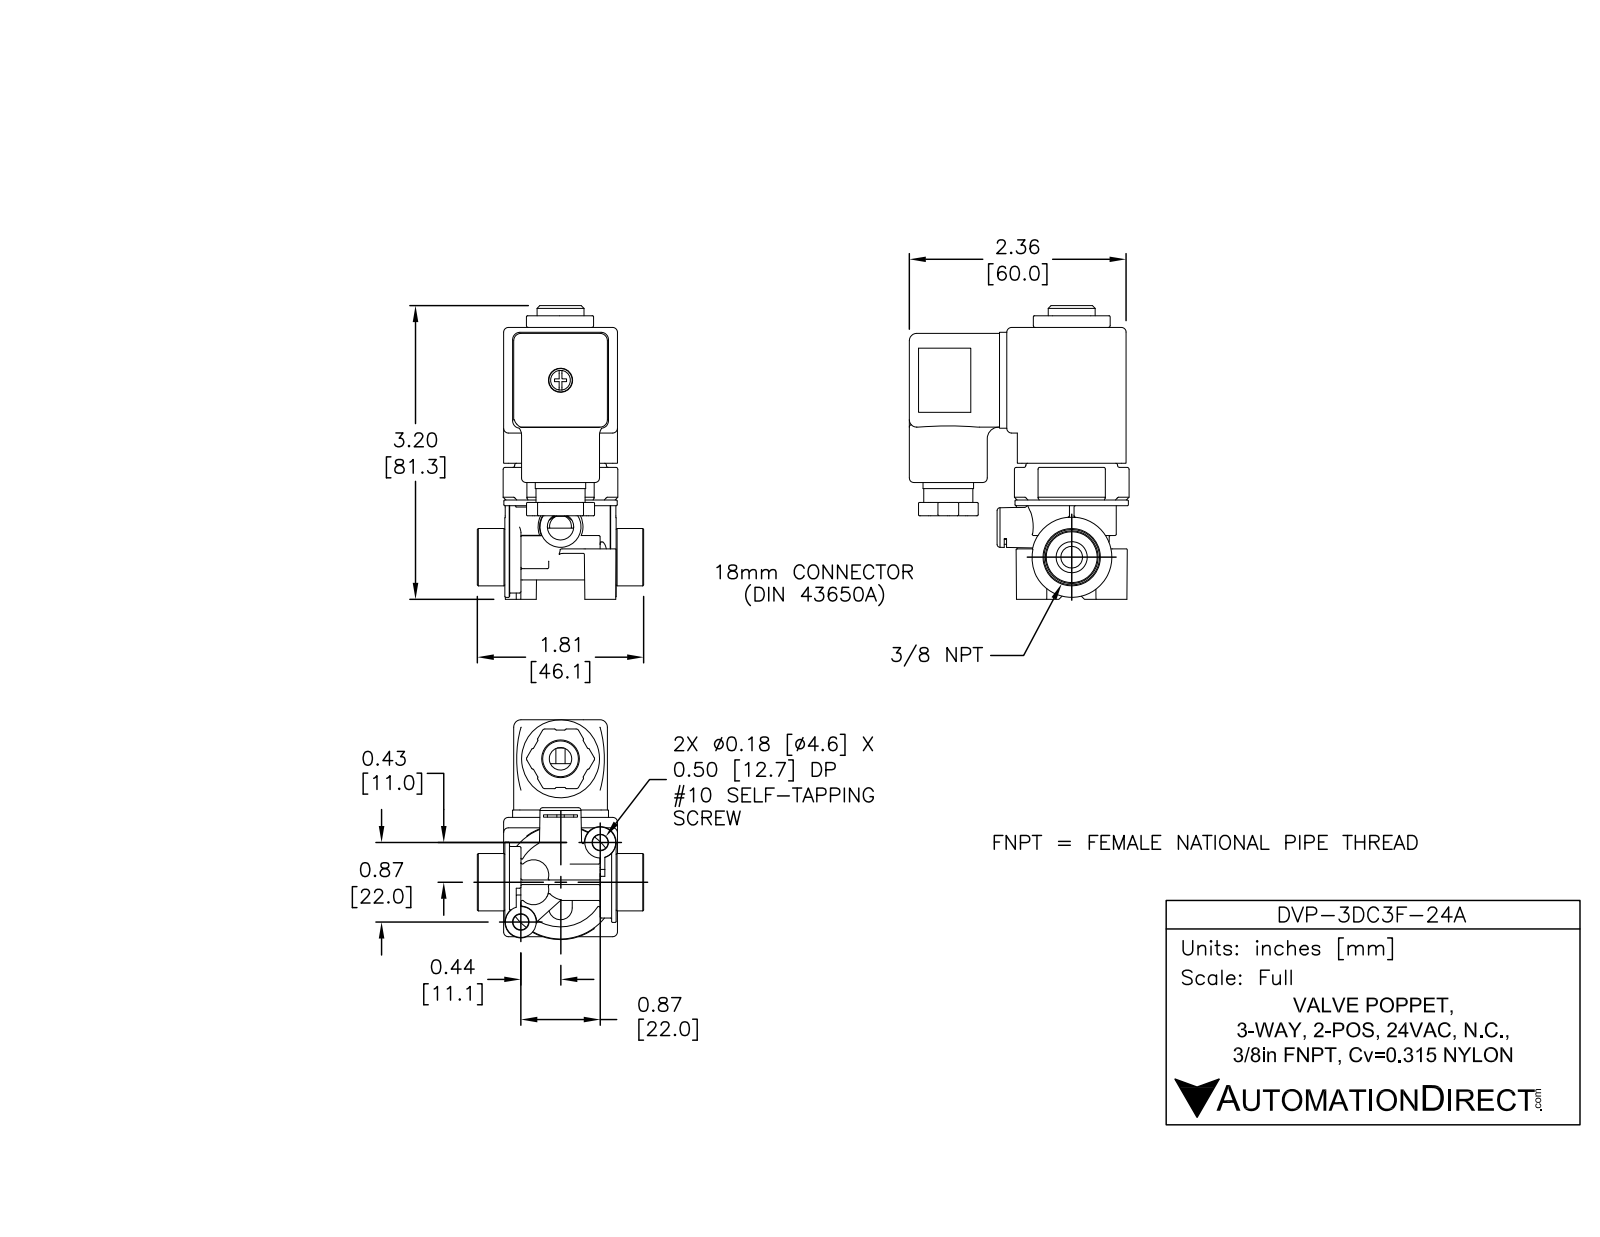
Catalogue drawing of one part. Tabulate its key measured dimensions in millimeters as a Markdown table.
| quantity | value |
| --- | --- |
| part name | DVP-3DC3F-24A |
| STEP written by | SolidWorks 2015 (AUTOMOTIVE_DESIGN) |
| units | millimeters |
| bodies | 6 solids, 1790 faces (806 planar, 344 cylindrical, 640 other) |
| overall size | 81.4 × 60.8 × 46.1 |
| volume | 64 240 mm³ |
| surface area | 35 660 mm² |
| round holes (diameter × count) | 1.5 × 2, 6 × 2, 2.4 × 1, 2.4 × 1, 2.6 × 1, 3 × 1, 3.5 × 1, 5.2 × 1, 6.2 × 1, 6.4 × 1, 6.7 × 1, 7.3 × 1 |
| round bosses / shafts (diameter × count) | 7.4 × 2, 31.4 × 1, 25.4 × 1, 24.7 × 1, 22.6 × 1, 22.2 × 1, 22.2 × 1, 21.6 × 1 |
| partial cylindrical surfaces (radius × count) | 0.3 × 74, 0.4 × 34, 1.3 × 21, 0.5 × 12, 2 × 12, 0.7 × 6, 0.8 × 6, 1 × 4 |
| main face-to-face distances | 27.5, 31.5, 1.2, 4, 2, 23.5, 36, 37.6, 2.8, 28.7 |
| hole center spacings | 7.1, 7.2, 27, 34.1, 34.2, 40.9, 41.3, 55.5 |
